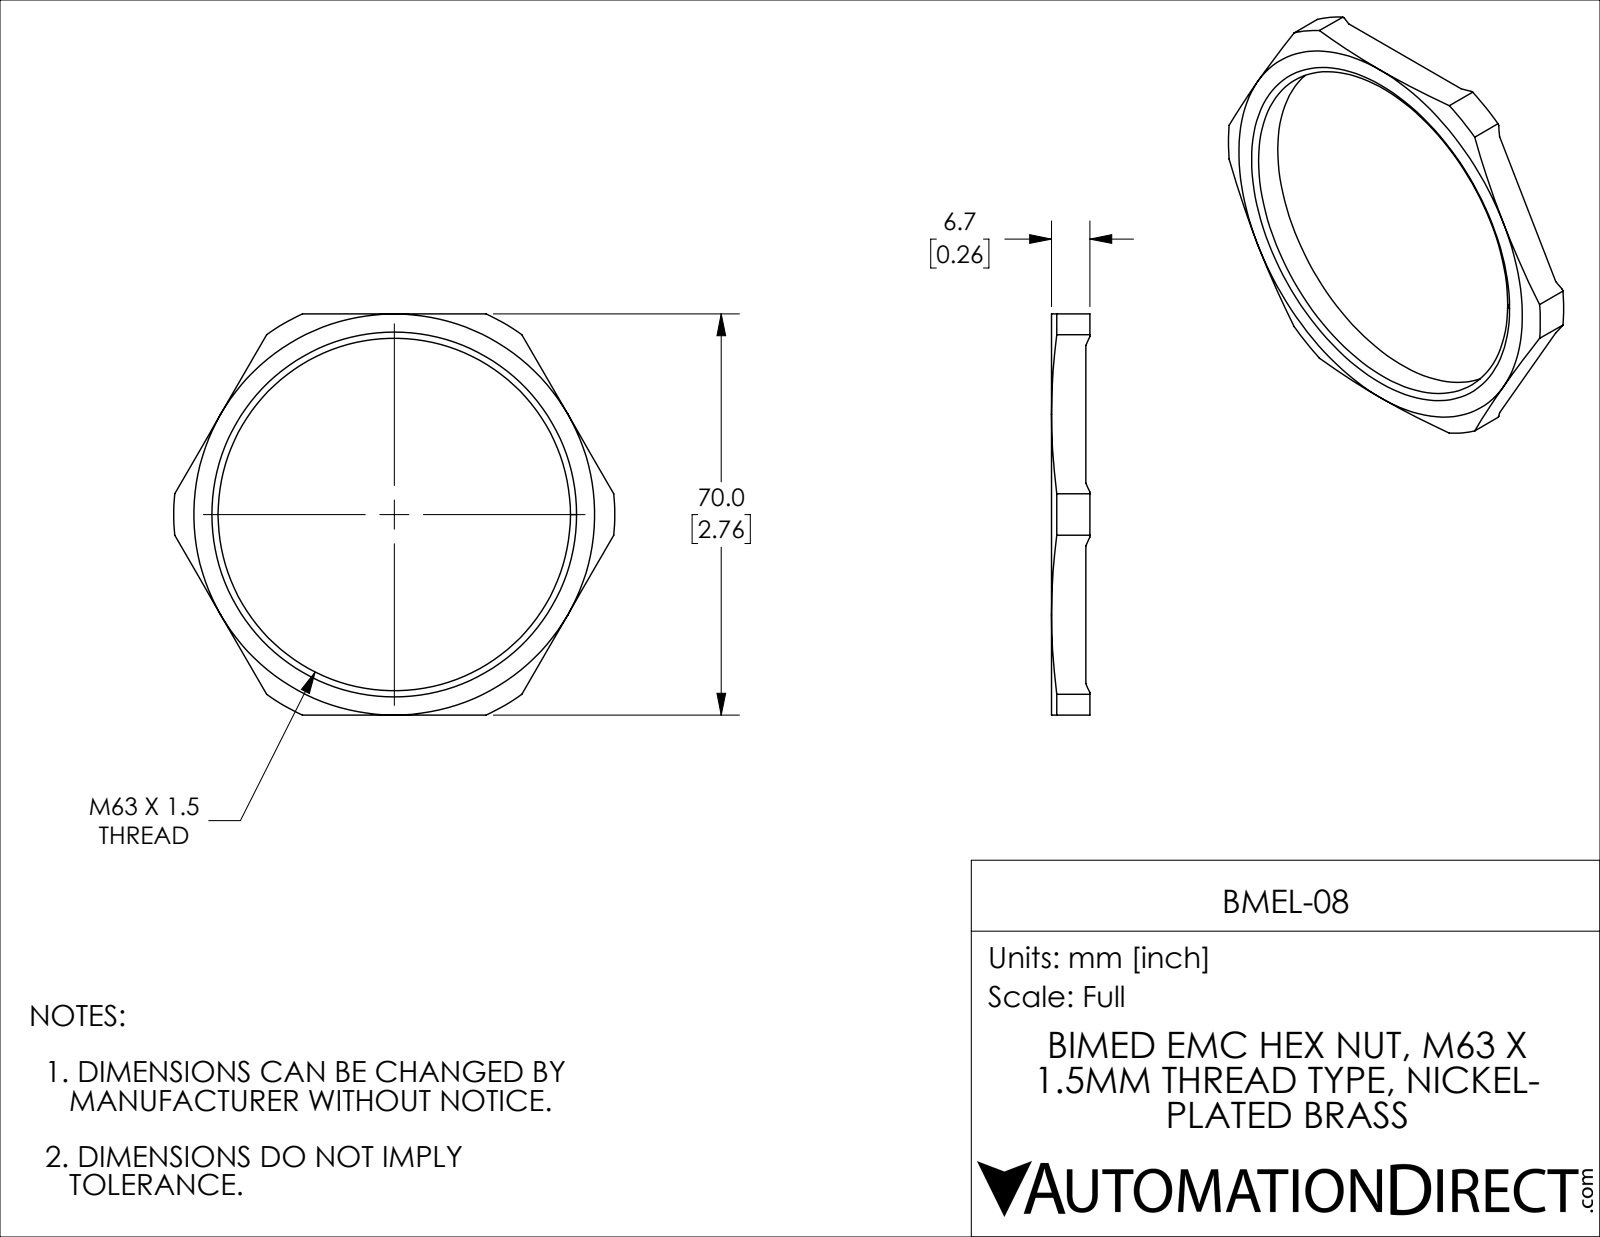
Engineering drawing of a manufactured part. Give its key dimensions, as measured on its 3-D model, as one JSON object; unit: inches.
{"part_name": "BMEL-08", "step_written_by": "SolidWorks 2021 (CONFIG_CONTROL_DESIGN)", "units": "inches", "bodies": {"solids": 1, "faces": 46, "planar": 14, "cylindrical": 8, "other": 24}, "overall_size": [3.031, 2.756, 0.264], "volume_in3": 0.436, "surface_area_in2": 7.48, "round_holes": [[2.422, 1]], "partial_cylinders_radius": [[1.516, 1]], "face_to_face_distances": [0.236, 2.756, 0.028, 0.264]}
